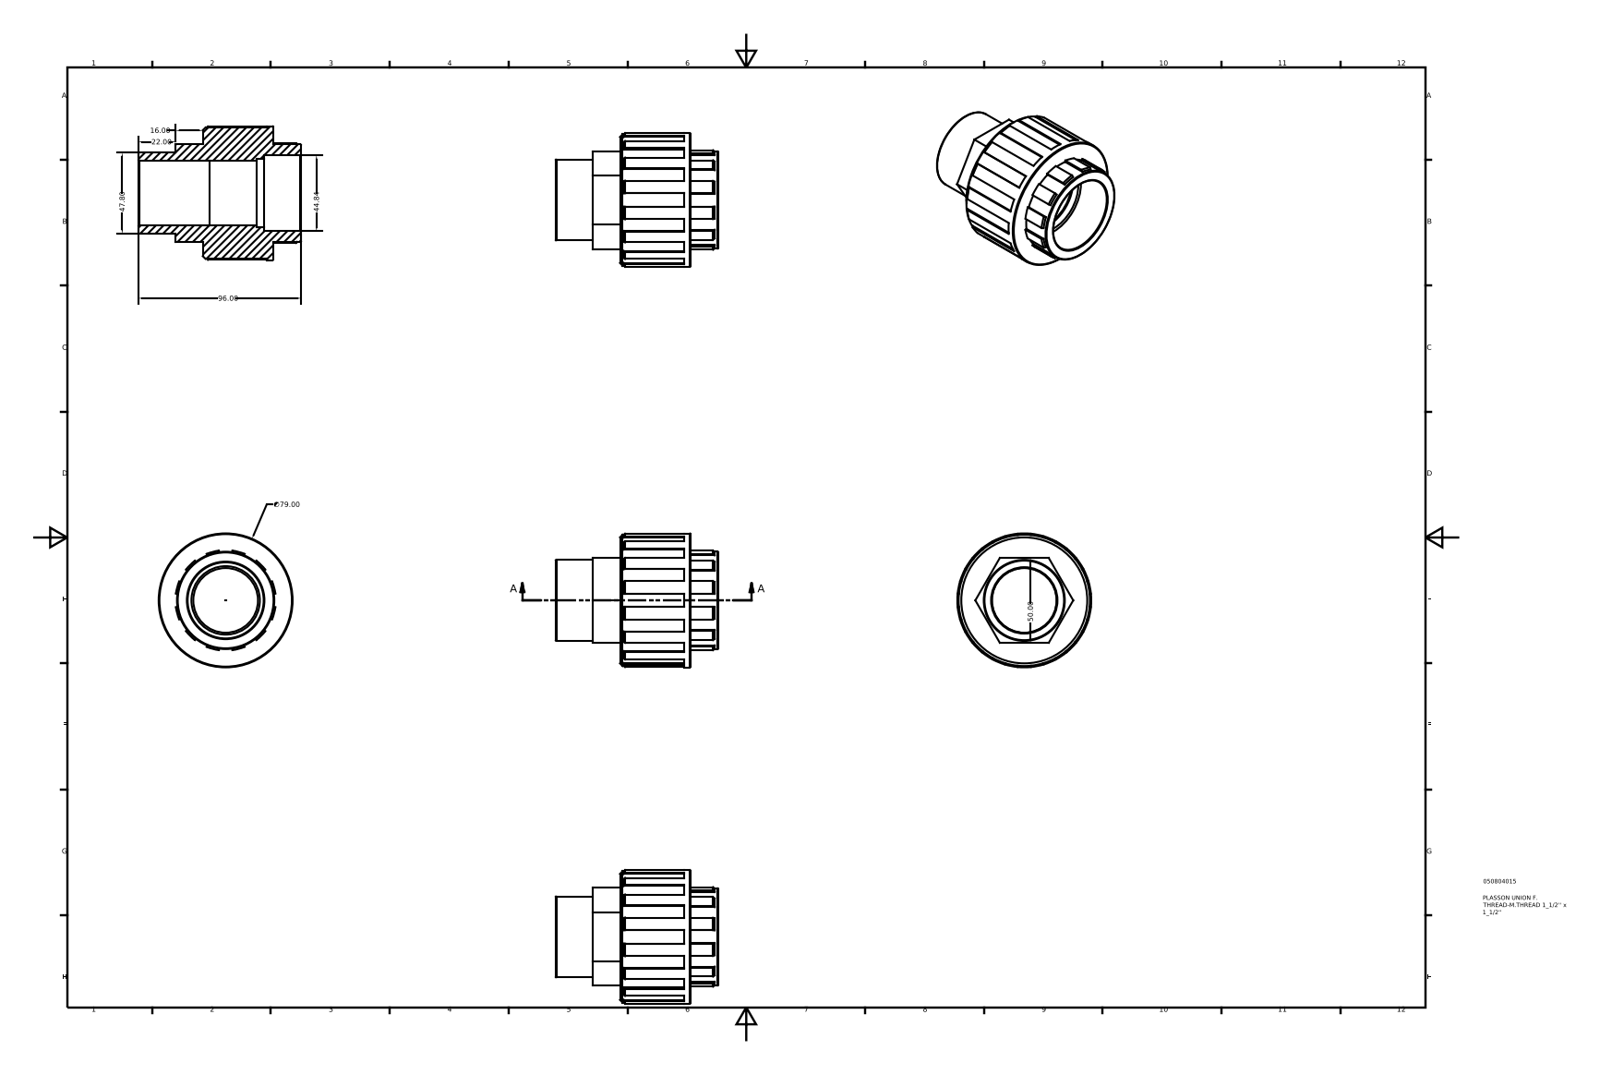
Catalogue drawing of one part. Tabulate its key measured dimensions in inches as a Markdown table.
| quantity | value |
| --- | --- |
| part name | 050804015 |
| STEP written by | Autodesk Inventor 2015 (AUTOMOTIVE_DESIGN) |
| units | inches |
| bodies | 1 solid, 140 faces (86 planar, 20 cylindrical, 34 other) |
| overall size | 3.78 × 3.11 × 3.11 |
| volume | 12.02 in³ |
| surface area | 61.23 in² |
| round holes (diameter × count) | 1.501 × 1, 1.506 × 1, 1.589 × 1, 1.765 × 1 |
| round bosses / shafts (diameter × count) | 3.11 × 1, 3.048 × 1, 2.26 × 1, 1.882 × 1 |
| partial cylindrical surfaces (radius × count) | 1.165 × 1 |
| main face-to-face distances | 1.634, 1.969, 2.283, 0.65, 0.866, 2.913, 1.496, 3.13, 3.78, 0.63 |
